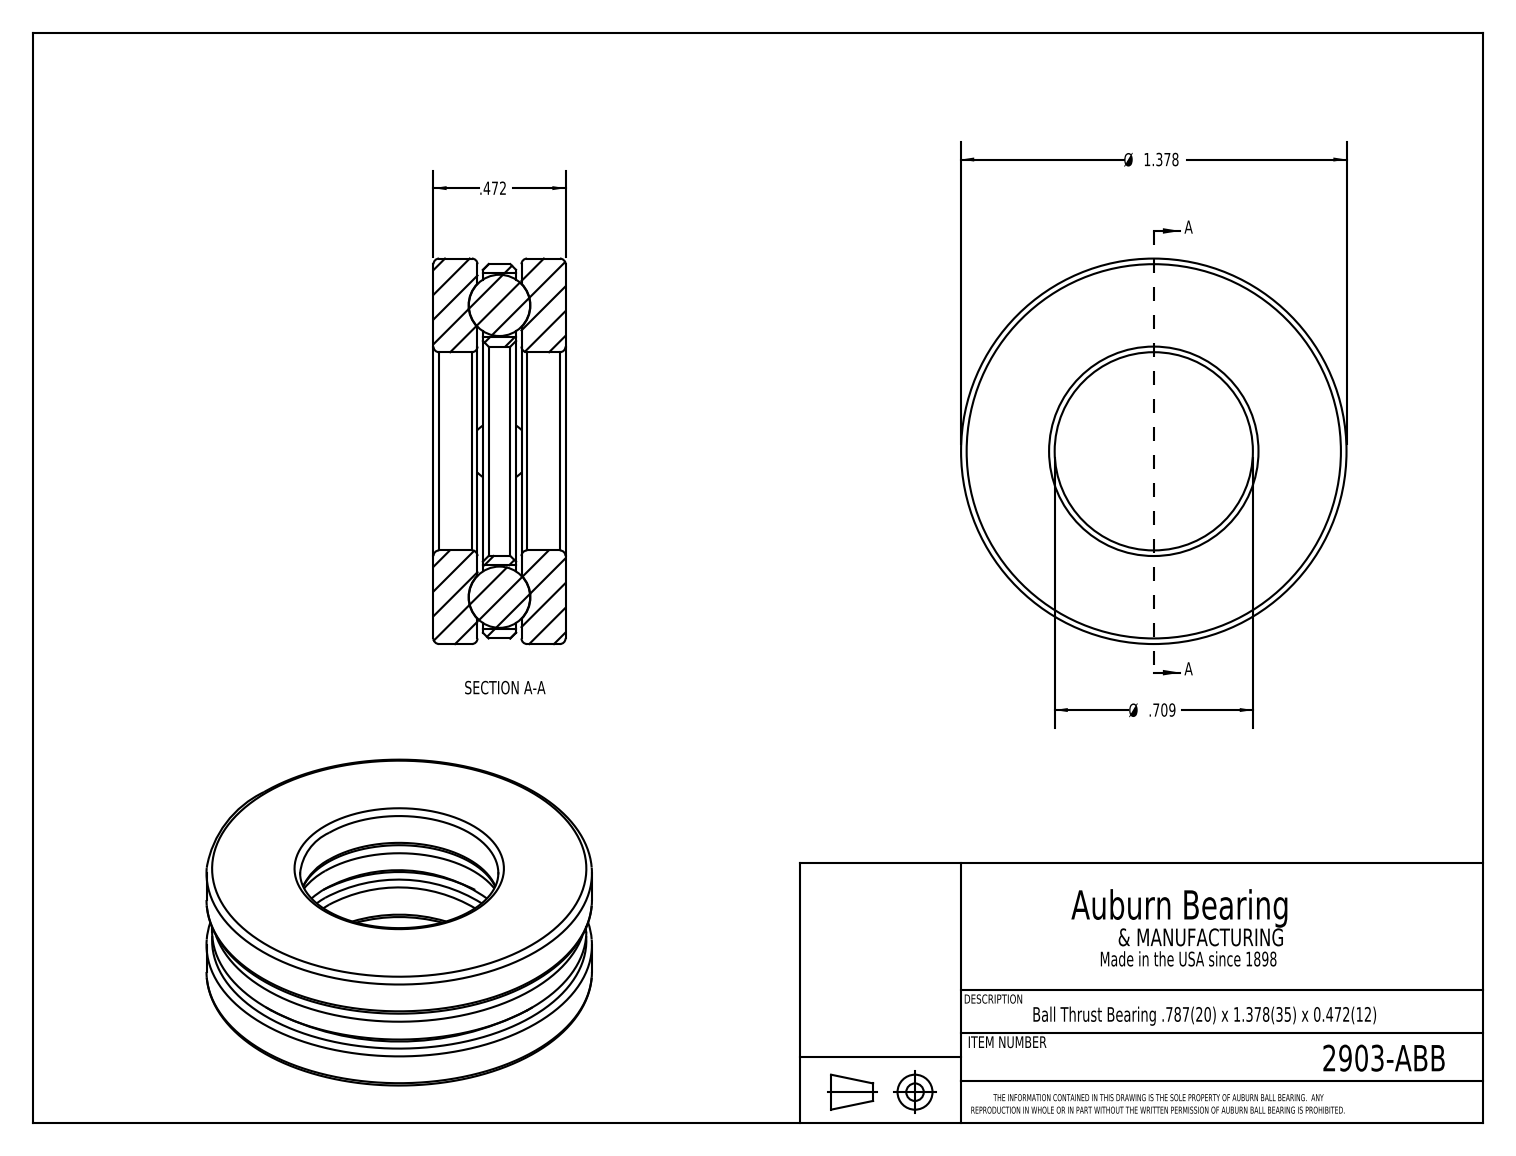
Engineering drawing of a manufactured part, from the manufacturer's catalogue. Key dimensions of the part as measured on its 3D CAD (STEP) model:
Part name (STEP PRODUCT): 2903-ABB
STEP written by: SolidWorks 2017 (CONFIG_CONTROL_DESIGN)
Units: inches
Bodies: 7 solids, 42 faces (14 planar, 10 cylindrical, 18 other)
Overall size (bounding box): 1.378 × 1.378 × 0.472
Volume: 0.394 in³ · Surface area: 9.022 in²
Round holes (diameter × count): ⌀0.229 ×4, ⌀0.787 ×1, ⌀0.827 ×1
Round bosses / shafts (diameter × count): ⌀1.378 ×1, ⌀1.338 ×1
Main face-to-face distances: 0.177, 0.295, 0.472, 0.157, 0.315, 0.02, 0.138, 0.118, 0.157
Hole centre spacings: 0.541, 0.766, 1.083
